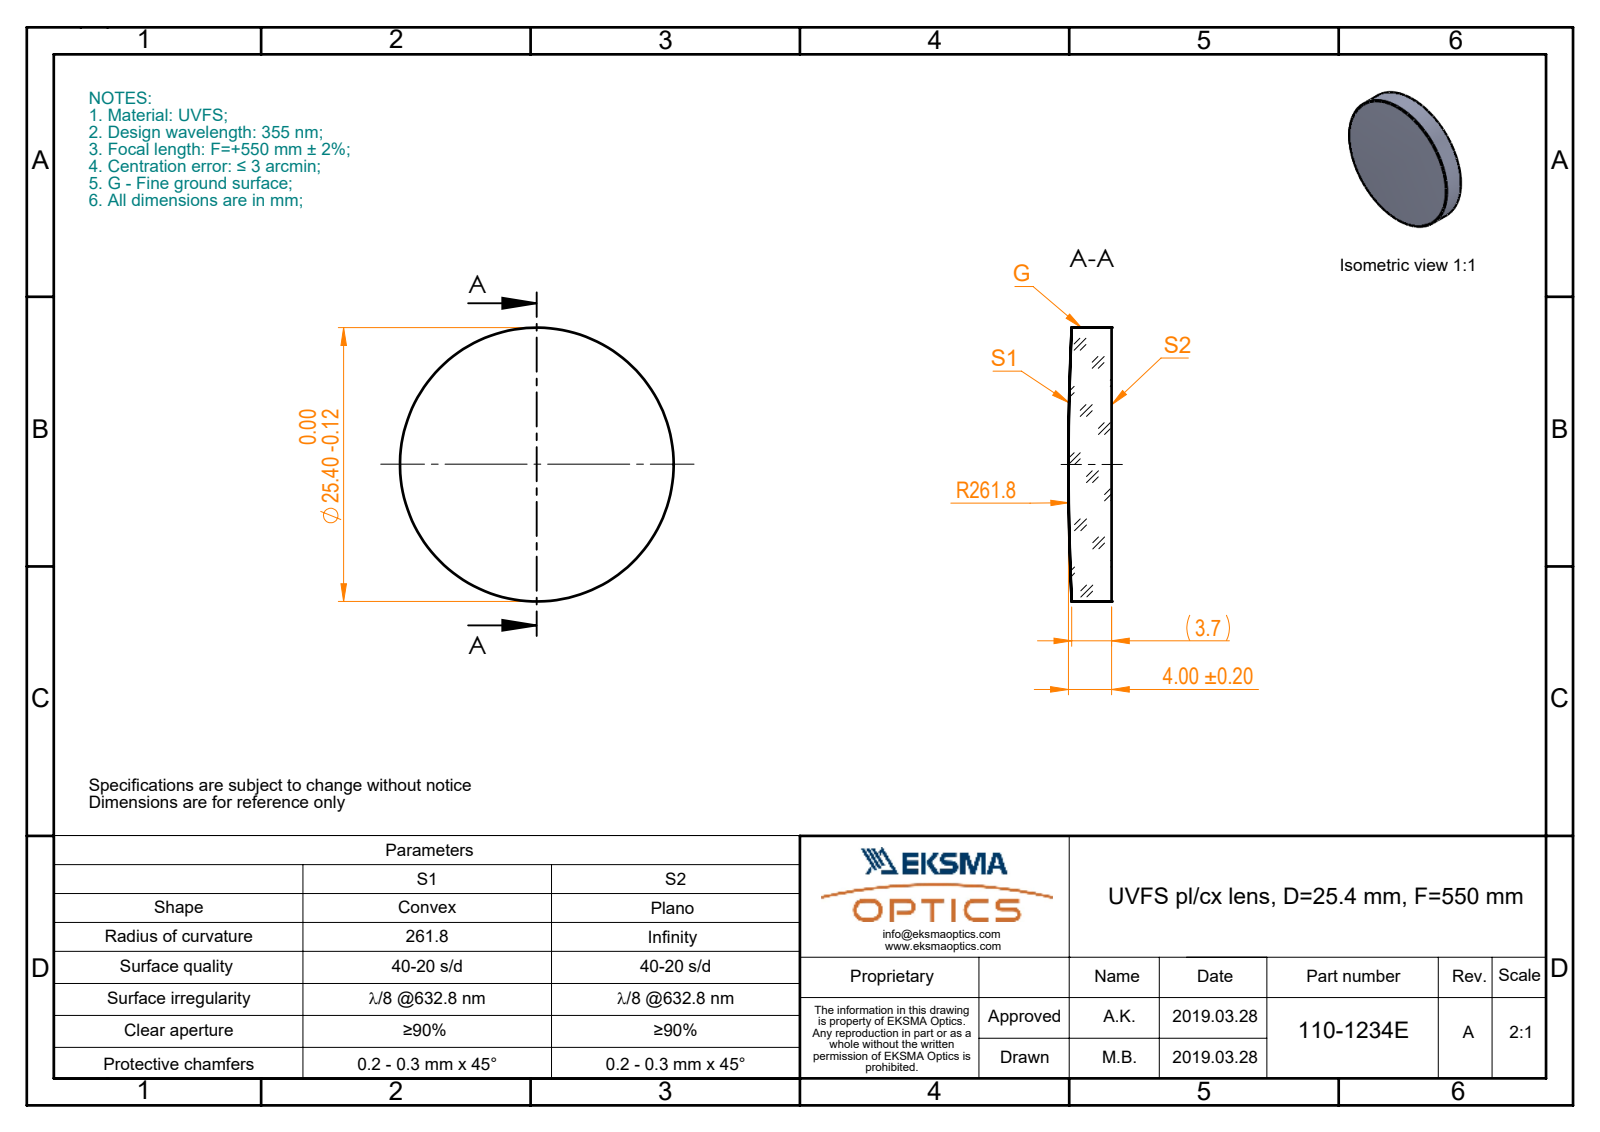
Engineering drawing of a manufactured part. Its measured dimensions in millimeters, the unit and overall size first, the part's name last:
Units: millimetres
Overall size (bounding box): 25.4 × 25.4 × 4
Round bosses / shafts (diameter × count): ⌀25.4 ×1
Volume: 1 949 mm³ · Surface area: 1 308 mm²
Bodies: 1 solid, 5 faces (1 planar, 2 cylindrical, 2 other)
Part name (STEP PRODUCT): 110-1234E UVFS pl-cx 25.4 F550
STEP written by: SolidWorks 2017 (CONFIG_CONTROL_DESIGN)
